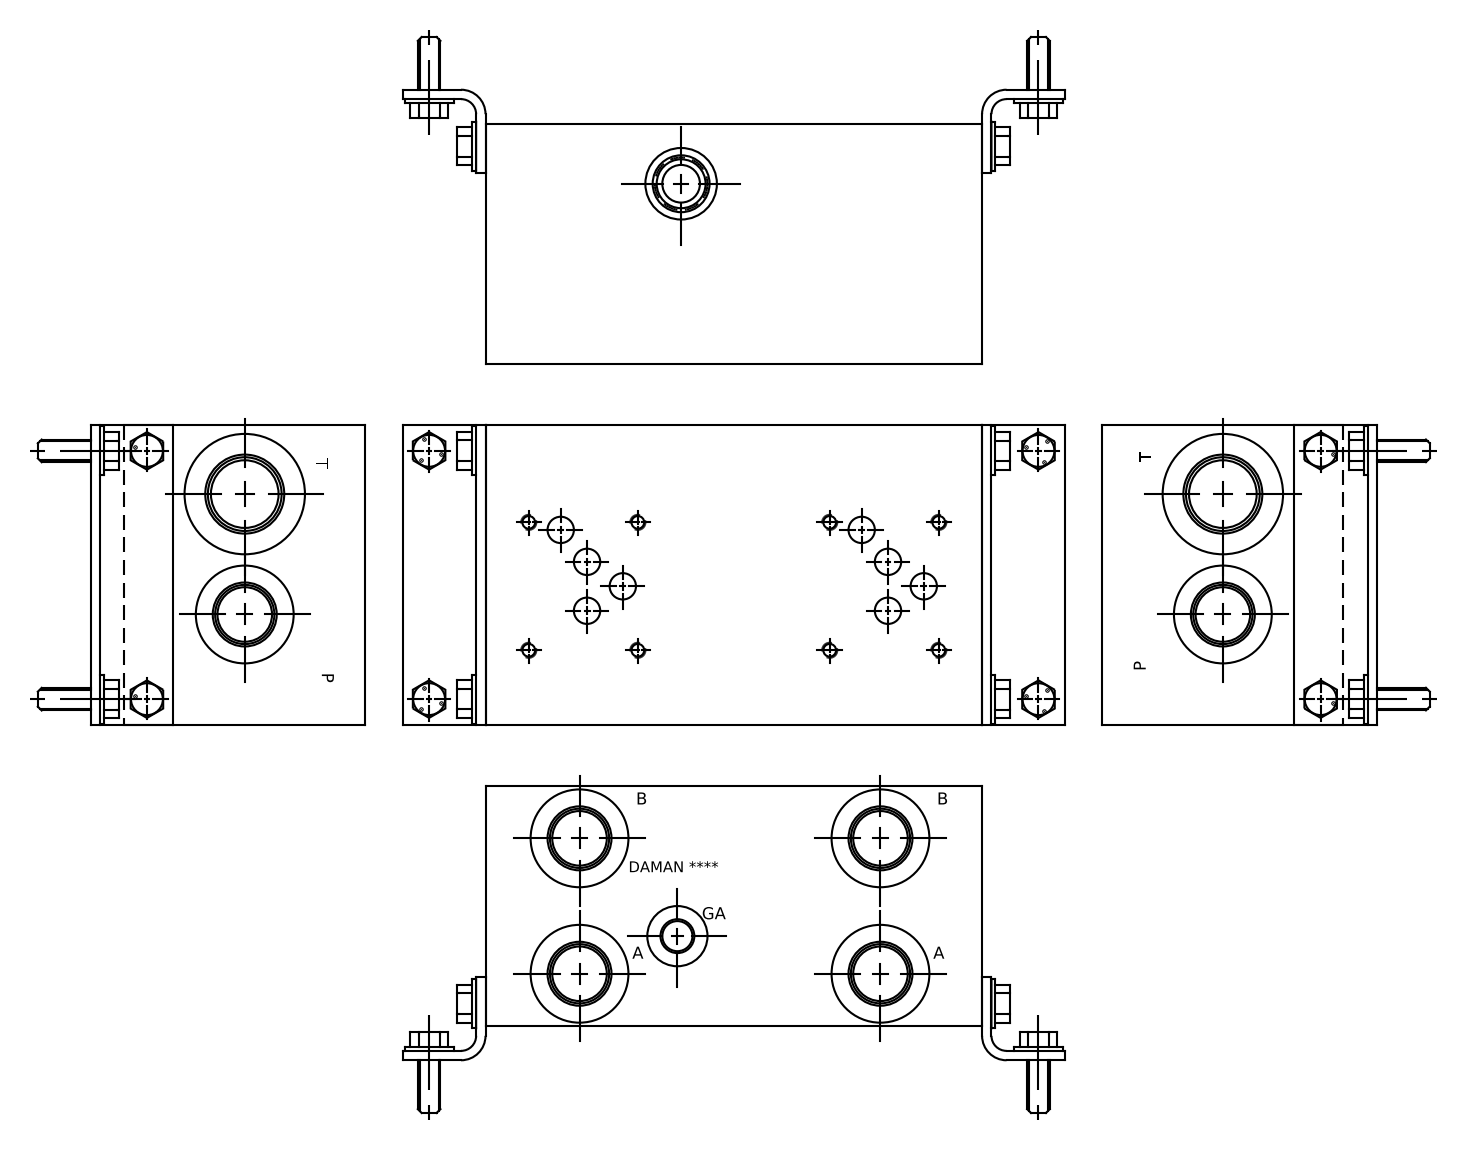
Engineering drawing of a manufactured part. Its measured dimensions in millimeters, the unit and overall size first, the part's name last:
Units: millimetres
Overall size (bounding box): 209.55 × 127 × 101.6
Round holes (diameter × count): ⌀5.11 ×8, ⌀6.35 ×8, ⌀11.13 ×6, ⌀23.01 ×5, ⌀24.92 ×5, ⌀27.43 ×5, ⌀42.04 ×5, ⌀27 ×4, ⌀7.92 ×2, ⌀9.53 ×2, ⌀11.11 ×2, ⌀26.99 ×2
Main face-to-face distances: 101.6, 127, 209.55, 0.79, 126.21, 208.76, 207.97, 19.05, 19.84, 189.71
Hole centre spacings: 127, 46.05, 70.95, 29.74, 43, 53.98, 138, 13.88
Volume: 2 505 000 mm³ · Surface area: 155 212 mm²
Bodies: 1 solid, 698 faces (376 planar, 84 cylindrical, 238 other)
Part name (STEP PRODUCT): Part_AD05HP025S~C_3D
STEP written by: Autodesk Inventor 2019 (AUTOMOTIVE_DESIGN)
